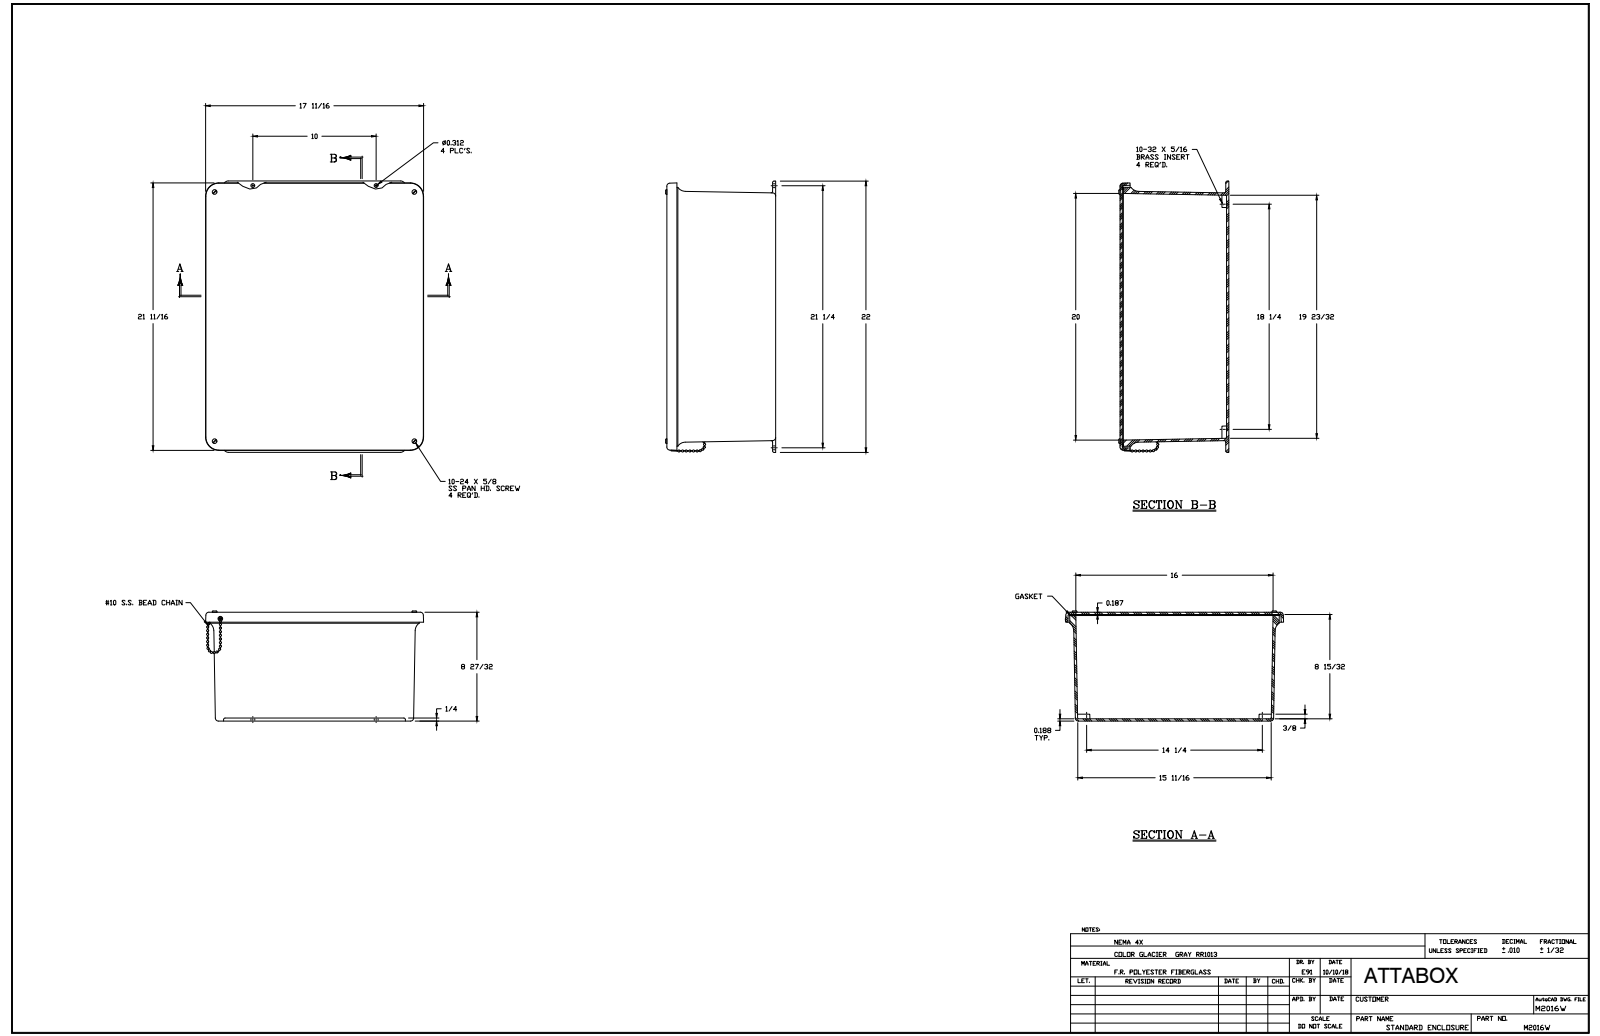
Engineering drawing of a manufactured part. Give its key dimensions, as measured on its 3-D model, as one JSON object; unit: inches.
{"part_name": "M2016W", "step_written_by": "SolidWorks 2018 (AUTOMOTIVE_DESIGN)", "units": "inches", "bodies": {"solids": 45, "faces": 883, "planar": 189, "cylindrical": 289, "other": 405}, "overall_size": [22.356, 17.845, 8.945], "volume_in3": 282, "surface_area_in2": 2882, "round_holes": [[0.14, 7], [0.152, 5], [0.145, 4], [0.156, 4], [0.218, 4], [0.187, 2], [0.126, 1]], "round_bosses_or_shafts": [[0.27, 8], [0.19, 4], [0.156, 4], [0.375, 2], [0.25, 2], [0.125, 2], [0.283, 1]], "partial_cylinders_radius": [[0.031, 20], [0.125, 10], [0.2, 10], [0.25, 8], [0.062, 4], [0.375, 4], [0.75, 4], [0.01, 2]], "face_to_face_distances": [0.187, 8.627, 8.814, 0.188, 8.439, 8.626, 0.313, 0.5, 0.064, 0.252], "hole_center_spacings": [1.381, 3.75, 15.257, 19.251, 24.526, 11, 7.25, 7.5]}
